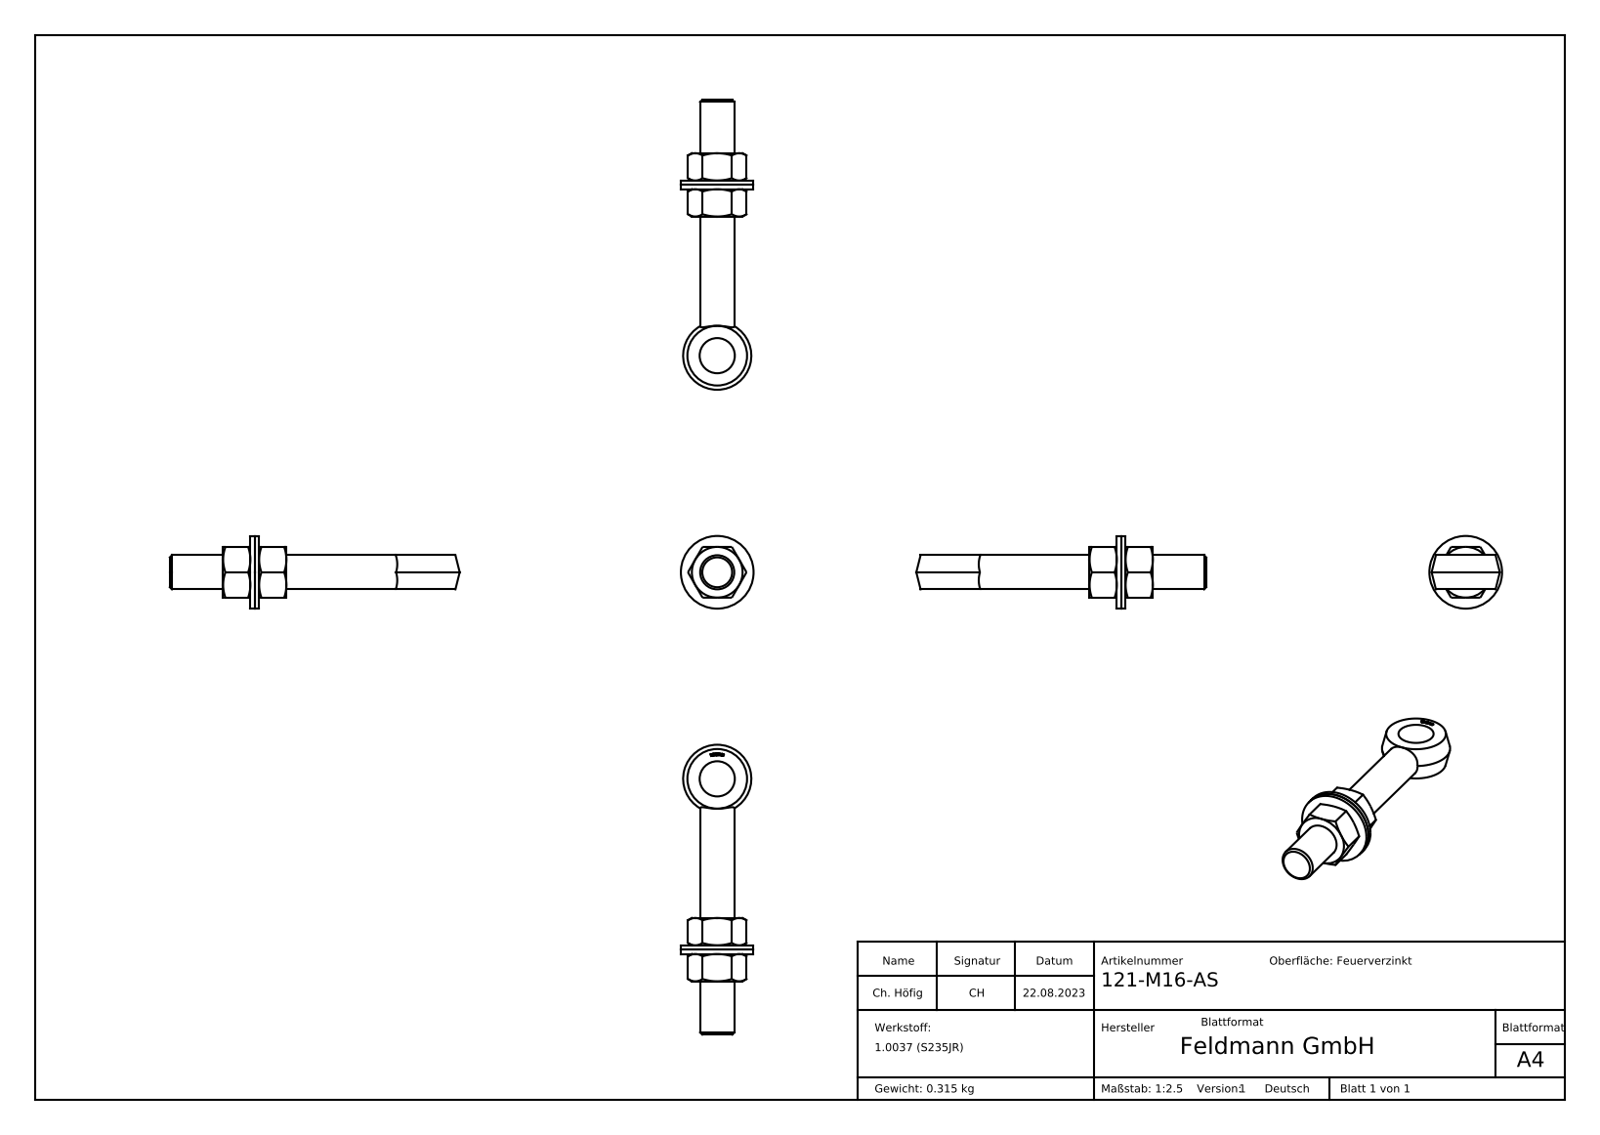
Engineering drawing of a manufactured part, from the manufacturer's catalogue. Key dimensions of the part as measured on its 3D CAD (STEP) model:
Part name (STEP PRODUCT): 121-Mxx-AS Teil2_121-M16-AS Teil2; 121-Mxx-AS Teil1_121-M16-AS Teil1; 121-Mxx-AS Teil3_121-M16-AS Teil3; 121-M16-AS
STEP written by: SolidWorks 2018 (CONFIG_CONTROL_DESIGN)
Units: millimetres
Bodies: 5 solids, 165 faces (96 planar, 8 cylindrical, 61 other)
Overall size (bounding box): 136 × 34.1 × 34.1
Volume: 40 356 mm³ · Surface area: 16 338 mm²
Round holes (diameter × count): ⌀14 ×1, ⌀16.3 ×1, ⌀16.5 ×1
Round bosses / shafts (diameter × count): ⌀34.1 ×1, ⌀16 ×1
Main face-to-face distances: 2, 2.1, 23.8, 4.1, 3.9, 19.9, 12.8, 14.8, 14.9, 16.9
